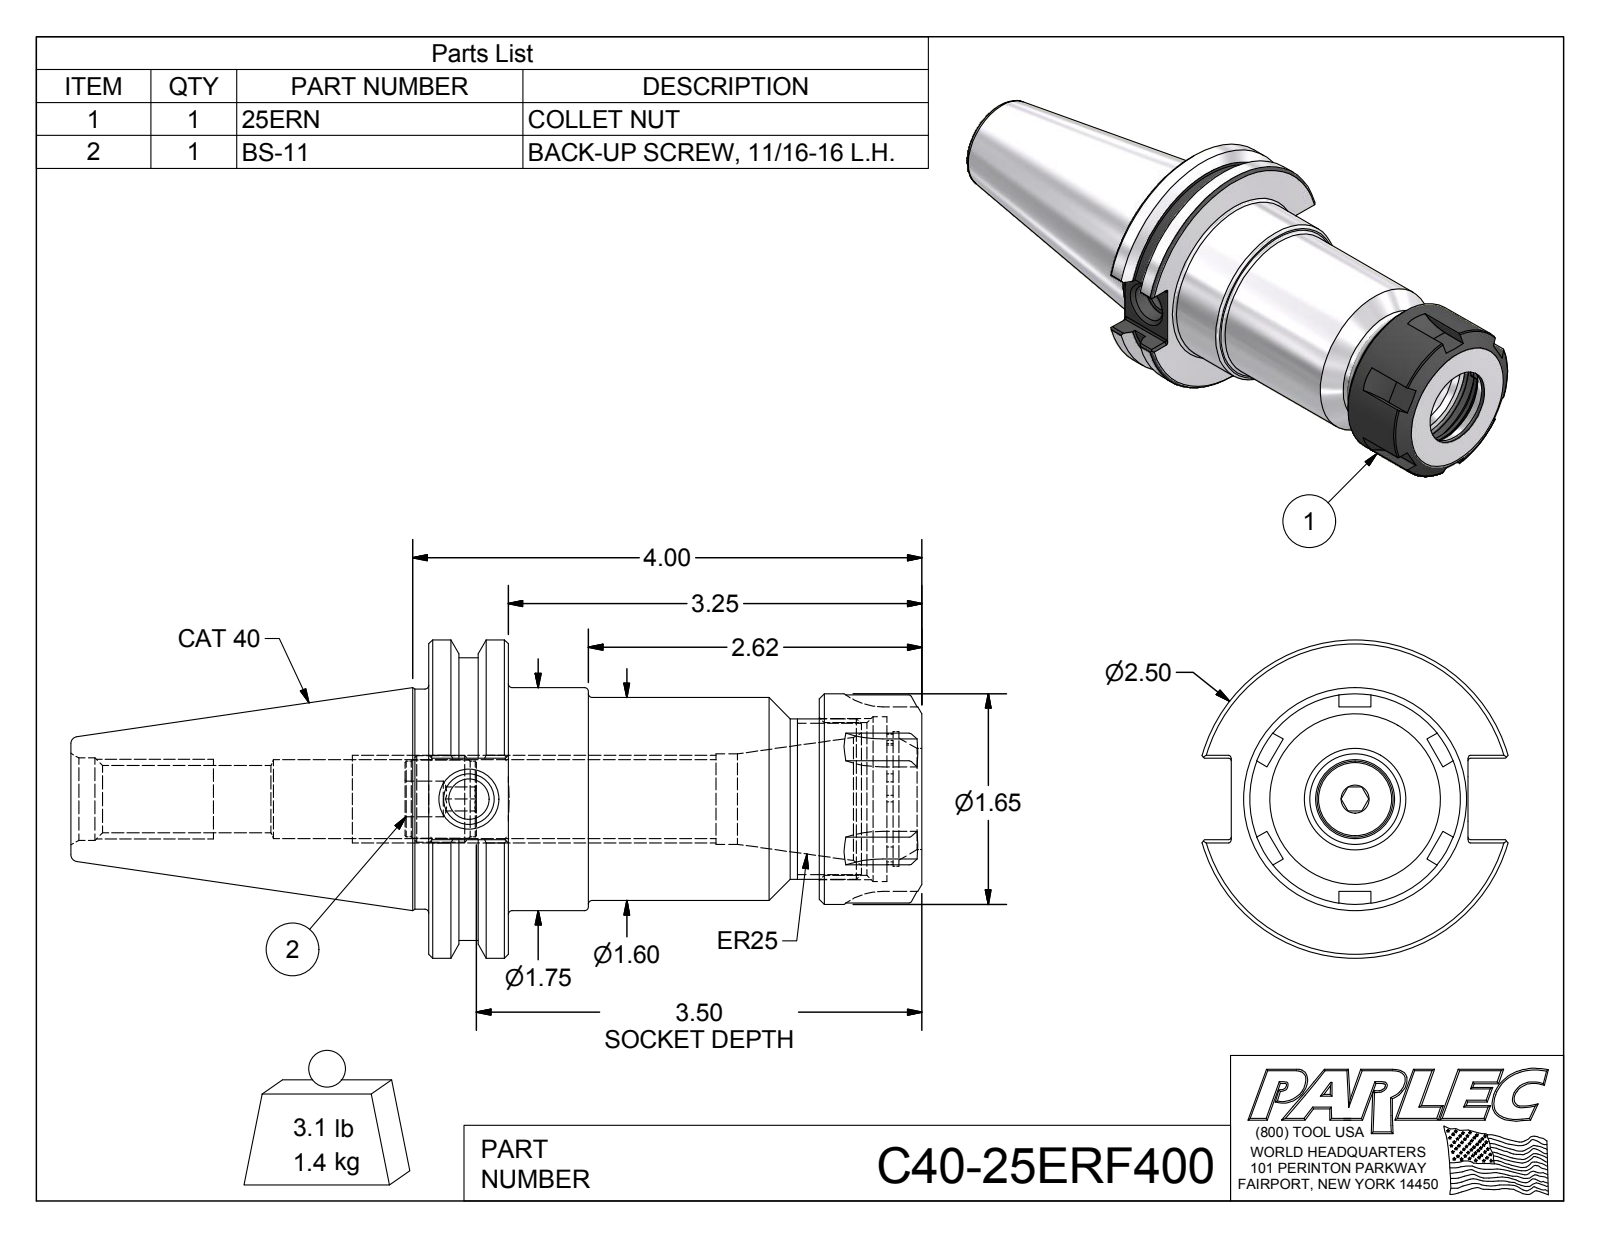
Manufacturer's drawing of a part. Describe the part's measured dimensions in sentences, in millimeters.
The part is named "C40-25ER4-1; 25ERN; BS-11; C40-25ERF400". Its 3-D file was written by "Autodesk Inventor 2016 (AUTOMOTIVE_DESIGN)". It is 3 solids with 187 faces: 76 planar, 51 cylindrical and 60 other. Overall it measures 169.86 by 63.5 by 61.05 millimeters. Its volume is 182 641 cubic millimeters and its surface area 40 548 square millimeters. Round holes: 1 of diameter 7.11, 1 of diameter 8, 1 of diameter 10.13, 1 of diameter 13.39, 1 of diameter 15.75, 1 of diameter 16.46, 1 of diameter 18.03, 1 of diameter 20.32, 1 of diameter 30.5, 1 of diameter 32.88. Round bosses or shafts: 1 of diameter 63.5, 1 of diameter 56.36, 1 of diameter 44.45, 1 of diameter 43.94, 1 of diameter 42, 1 of diameter 40.51, 1 of diameter 32, 1 of diameter 17.3. Partial cylindrical surfaces (rounded edges, fillets, slot ends): 24 of radius 0.51, 1 of radius 12, 1 of radius 13.06, 1 of radius 13.43. The main face-to-face distances are 15.88, 98.43, 82.55, 77.86, 61.98, 20.57, 91.33, 75.45, 13.47, 7.1.
